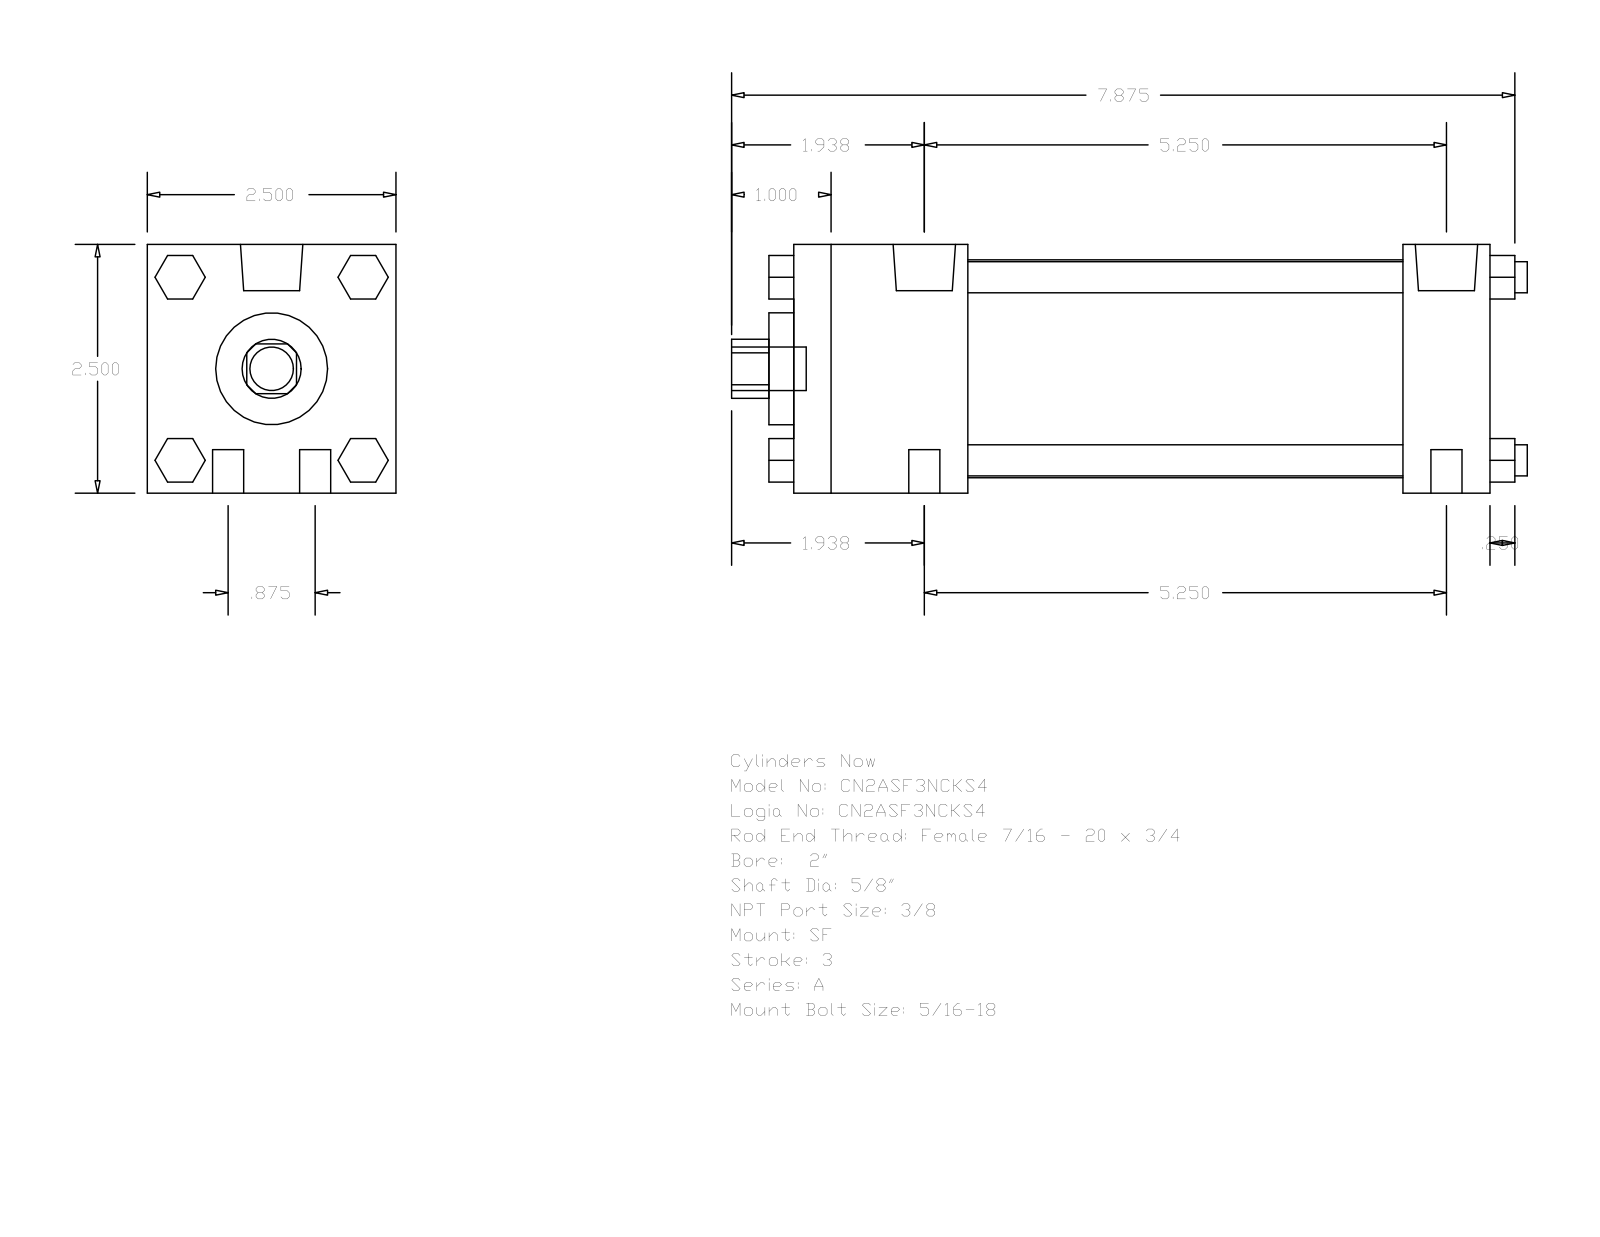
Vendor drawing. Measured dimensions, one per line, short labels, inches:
name: A_SF__0200_0.625
written by: GSSL Pune (CONFIG_CONTROL_DESIGN)
unit: in
bodies: 0 solids, 124 faces (94 planar, 30 cylindrical, 0 other)
size: 8 × 2.5 × 2.5
holes: 1× ⌀0.625, 1× ⌀1.125, 1× ⌀2.19
bosses: 8× ⌀0.313, 2× ⌀0.627, 2× ⌀0.219, 1× ⌀0.437
rounds: 1× R0.297
face distances: 2.5, 7, 6.125, 0.875, 1.75, 4.375, 5.25, 7.25, 0.25, 2
